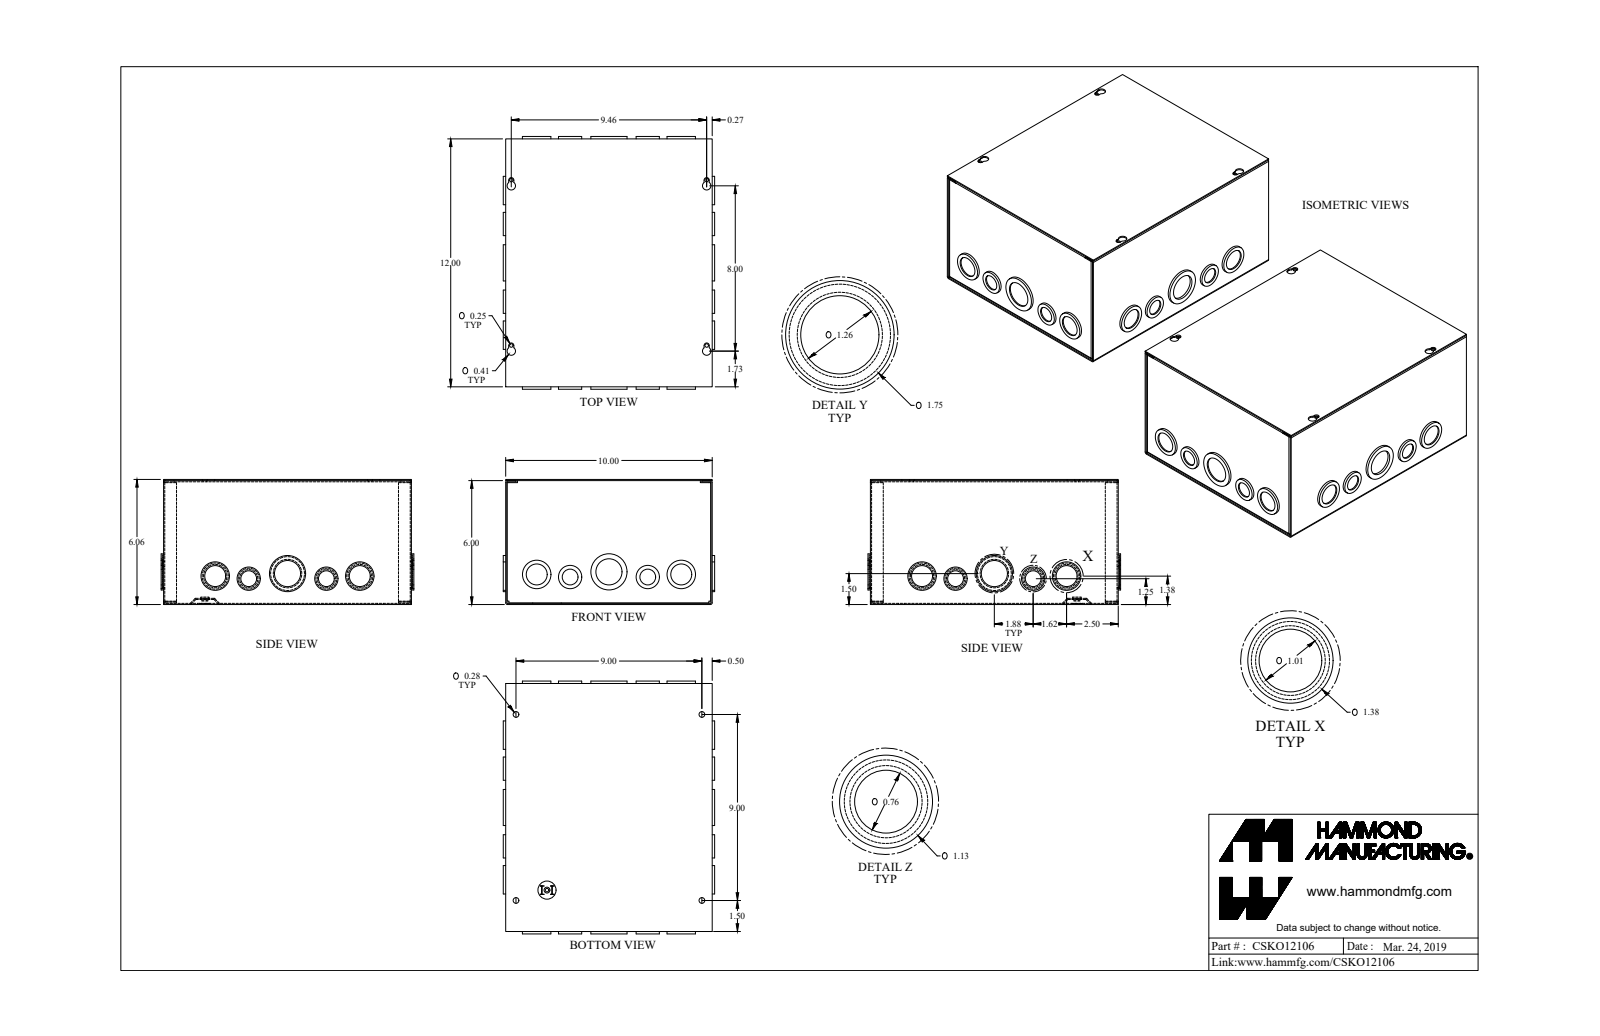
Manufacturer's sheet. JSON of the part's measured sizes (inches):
{"part_name": "CSKO12106_Default", "step_written_by": "SolidWorks 2019 (CONFIG_CONTROL_DESIGN)", "units": "inches", "bodies": {"solids": 4, "faces": 445, "planar": 205, "cylindrical": 232, "other": 8}, "overall_size": [12.234, 10.234, 6.057], "volume_in3": 31.48, "surface_area_in2": 1116, "round_holes": [[1.011, 8], [1.261, 6], [0.17, 5], [0.281, 4], [0.761, 4], [1.636, 2], [0.5, 1]], "round_bosses_or_shafts": [[1.125, 6], [1.375, 5], [0.875, 4], [0.875, 4], [1.375, 3], [1.75, 2], [1.125, 2], [0.492, 1]], "partial_cylinders_radius": [[0.029, 12], [0.086, 12], [0.057, 8], [0.125, 4], [0.203, 4]], "face_to_face_distances": [0.057, 6, 5.943, 9.943, 6.057, 11.943, 10, 9.886, 12, 11.886], "hole_center_spacings": [0.55, 1.625, 1.896, 3.502, 5.381, 8.503, 9, 9.243]}
